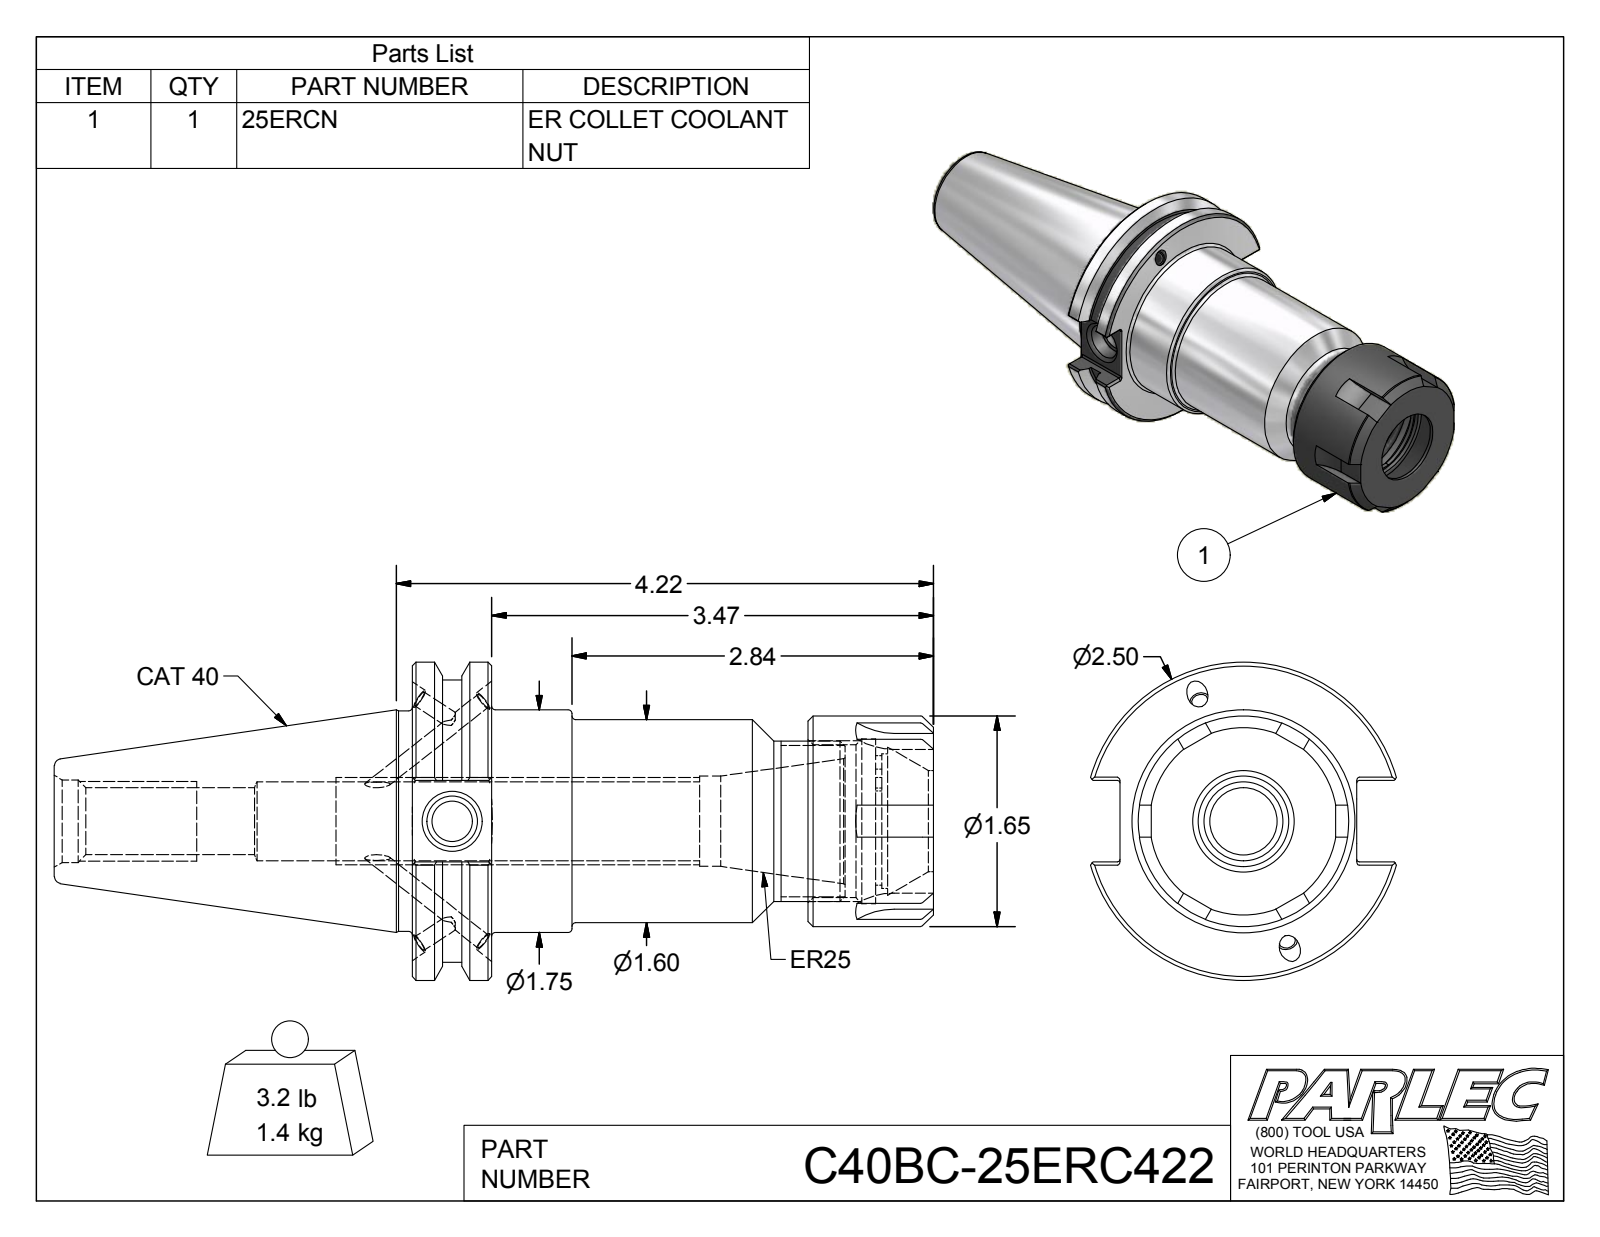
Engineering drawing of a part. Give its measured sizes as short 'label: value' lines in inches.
name: C40BCB-25ER4-1; 029-965; 25ERCN; C40BC-25ERC422
written by: Autodesk Inventor 2016 (AUTOMOTIVE_DESIGN)
unit: in
bodies: 6 solids, 225 faces (105 planar, 64 cylindrical, 56 other)
size: 6.907 × 2.5 × 2.404
volume: 11.19 in³; area: 64.38 in²
holes: 4× ⌀0.13, 4× ⌀0.161, 1× ⌀0.315, 1× ⌀0.399, 1× ⌀0.527, 1× ⌀0.62, 1× ⌀0.648, 1× ⌀0.71, 1× ⌀0.794, 1× ⌀1.057, 1× ⌀1.201, 1× ⌀1.294
bosses: 4× ⌀0.165, 4× ⌀0.157, 1× ⌀2.5, 1× ⌀2.219, 1× ⌀1.75, 1× ⌀1.73, 1× ⌀1.654, 1× ⌀1.595
rounds: 12× R0.02, 6× R0.5, 1× R0.472, 1× R0.515
face distances: 0.625, 4.095, 3.47, 3.111, 2.486, 0.984, 3.643, 3.017, 0.531, 0.453
